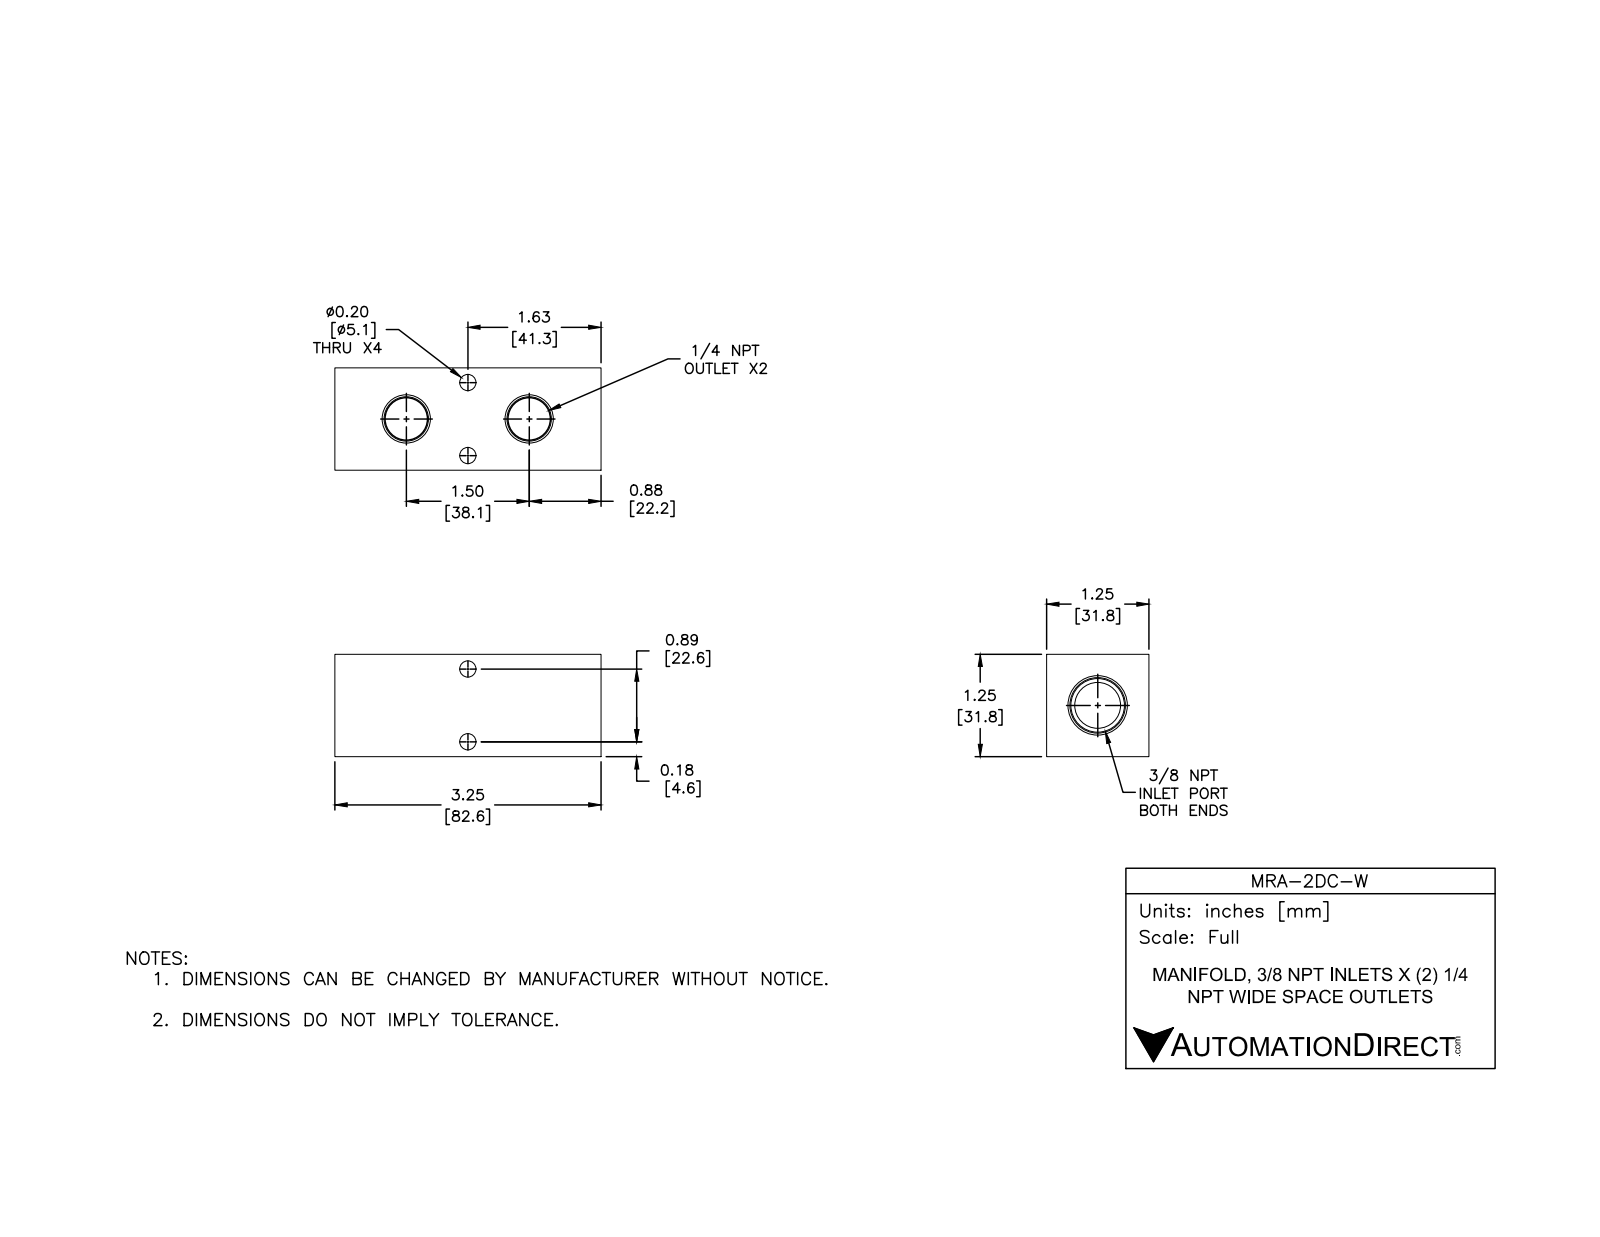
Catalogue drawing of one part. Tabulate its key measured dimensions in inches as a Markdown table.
| quantity | value |
| --- | --- |
| part name | MRA-2DC-W |
| STEP written by | SolidWorks 2015 (CONFIG_CONTROL_DESIGN) |
| units | inches |
| bodies | 1 solid, 58 faces (12 planar, 30 cylindrical, 16 other) |
| overall size | 3.25 × 1.25 × 1.25 |
| volume | 3.889 in³ |
| surface area | 27.5 in² |
| round holes (diameter × count) | 0.2 × 4, 0.562 × 1 |
| partial cylindrical surfaces (radius × count) | 0.219 × 2 |
| main face-to-face distances | 1.25, 3.25, 0.41, 2.84, 2.43, 0.86, 0.39 |
| hole center spacings | 0.89 |
